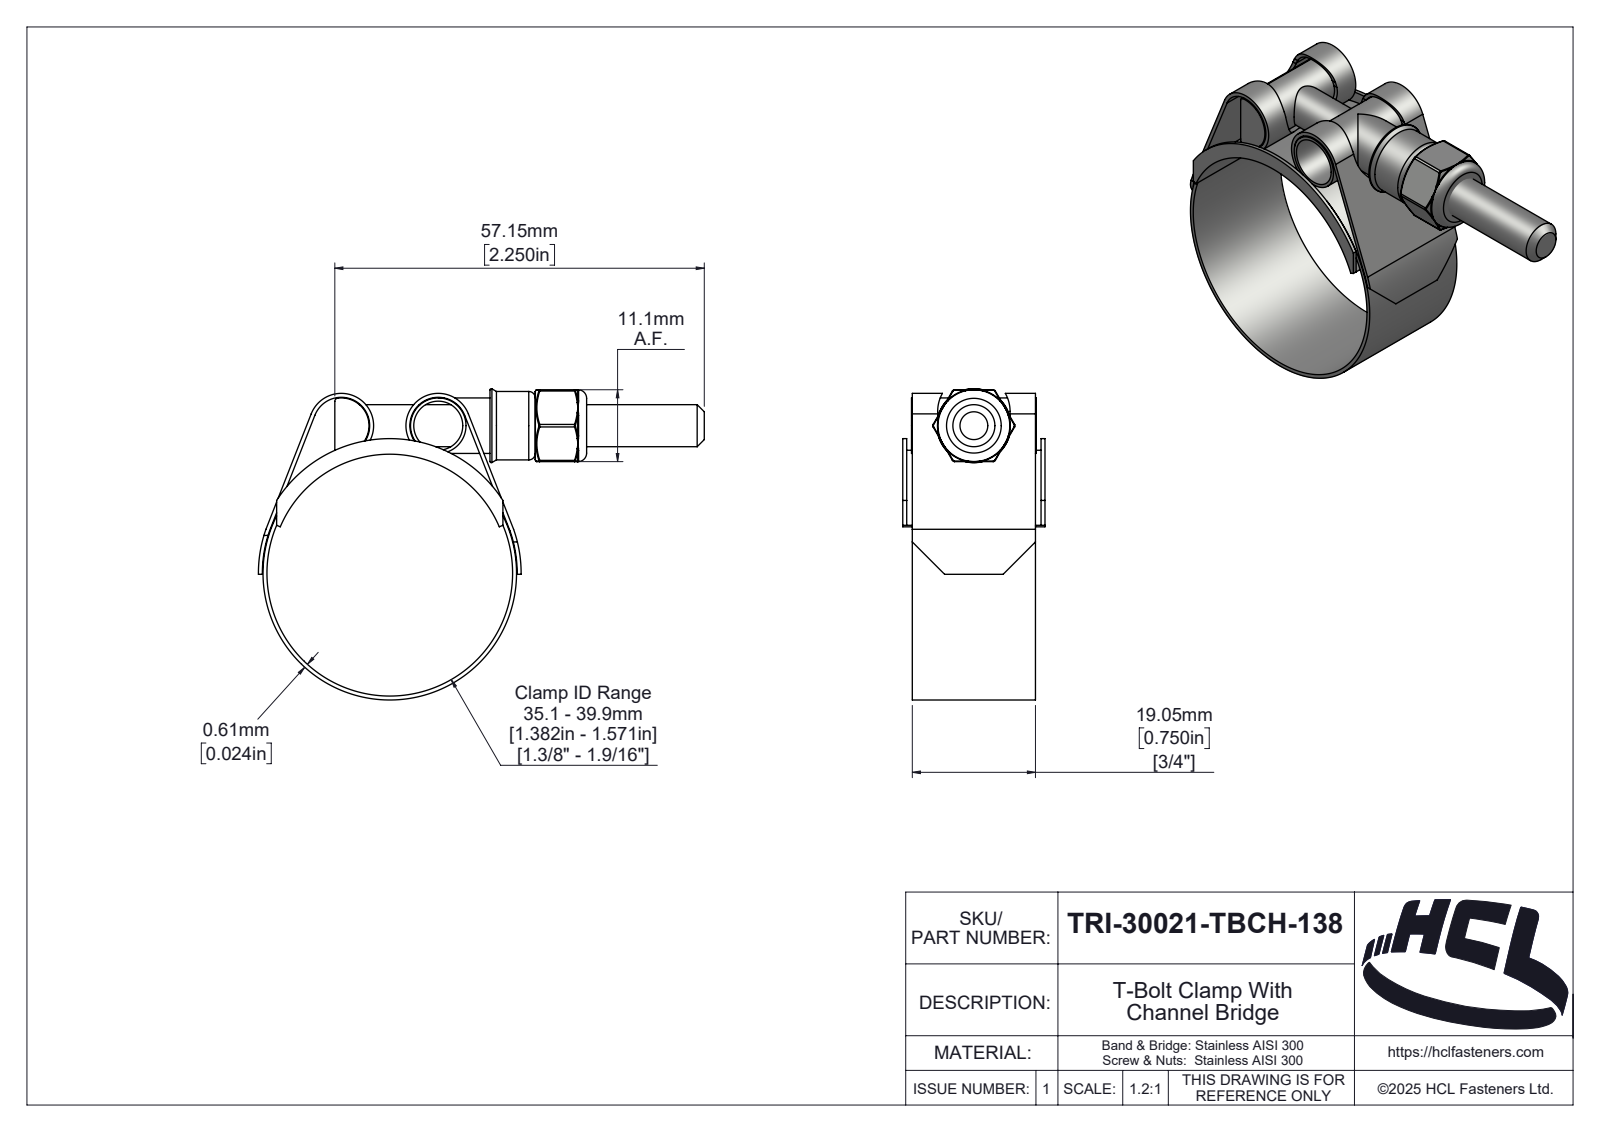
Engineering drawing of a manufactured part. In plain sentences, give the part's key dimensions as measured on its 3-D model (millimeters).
The part is named "TRI-30021-TBCH-138". Its 3-D file was written by "SolidWorks 2025 (AUTOMOTIVE_DESIGN)". It is 6 solids with 340 faces: 50 planar, 128 cylindrical and 162 other. Overall it measures 68.97 by 48.13 by 22 millimeters. Its volume is 6 426 cubic millimeters and its surface area 13 219 square millimeters. Round holes: 1 of diameter 5.4, 1 of diameter 6.35, 1 of diameter 6.5, 1 of diameter 7.58, 1 of diameter 38. Round bosses or shafts: 2 of diameter 8.58, 1 of diameter 39.22, 1 of diameter 10.58. Partial cylindrical surfaces (rounded edges, fillets, slot ends): 6 of radius 0.39, 2 of radius 0.5, 2 of radius 4.39, 2 of radius 5, 2 of radius 5.6, 1 of radius 0.59, 1 of radius 2.42, 1 of radius 3.03. The main face-to-face distances are 0.61, 1.47, 20.53, 0.74, 21.39, 0.86, 19.92, 19.06, 22, 1.35. The hole center spacings are 24.
